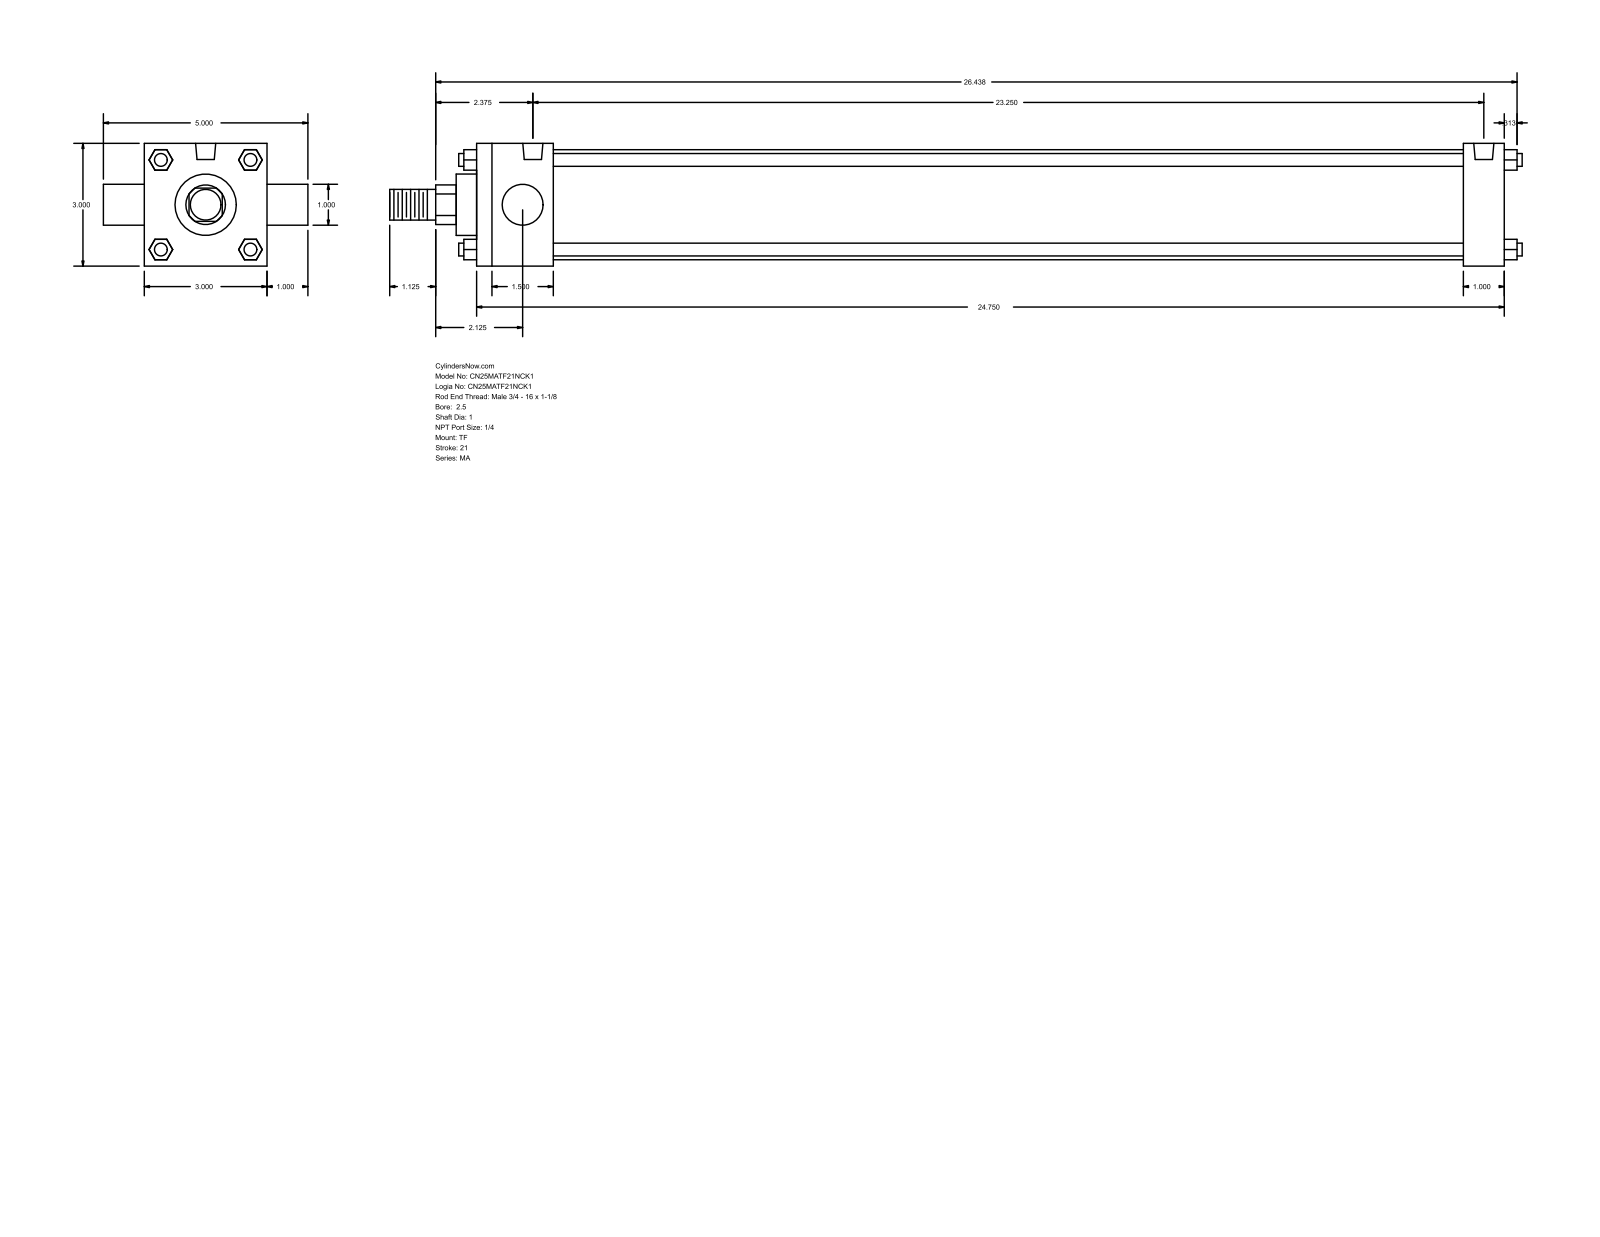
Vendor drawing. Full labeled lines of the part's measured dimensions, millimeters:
Part name (STEP PRODUCT): MA_TF__0250_1
STEP written by: GSSL Pune (CONFIG_CONTROL_DESIGN)
Units: millimetres
Bodies: 0 solids, 120 faces (92 planar, 28 cylindrical, 0 other)
Overall size (bounding box): 703.26 × 127 × 76.2
Round holes (diameter × count): ⌀7.94 ×3, ⌀12.49 ×2
Round bosses / shafts (diameter × count): ⌀7.94 ×4, ⌀25.4 ×2, ⌀68.33 ×1, ⌀38.1 ×1, ⌀19.05 ×1
Partial cylindrical surfaces — rounded edges, fillets, slot ends (radius × count): R12.29 ×1
Main face-to-face distances: 76.2, 638.18, 12.7, 47.63, 612.77, 565.14, 590.55, 25.41, 101.6, 25.4
Hole centre spacings: 590.55
